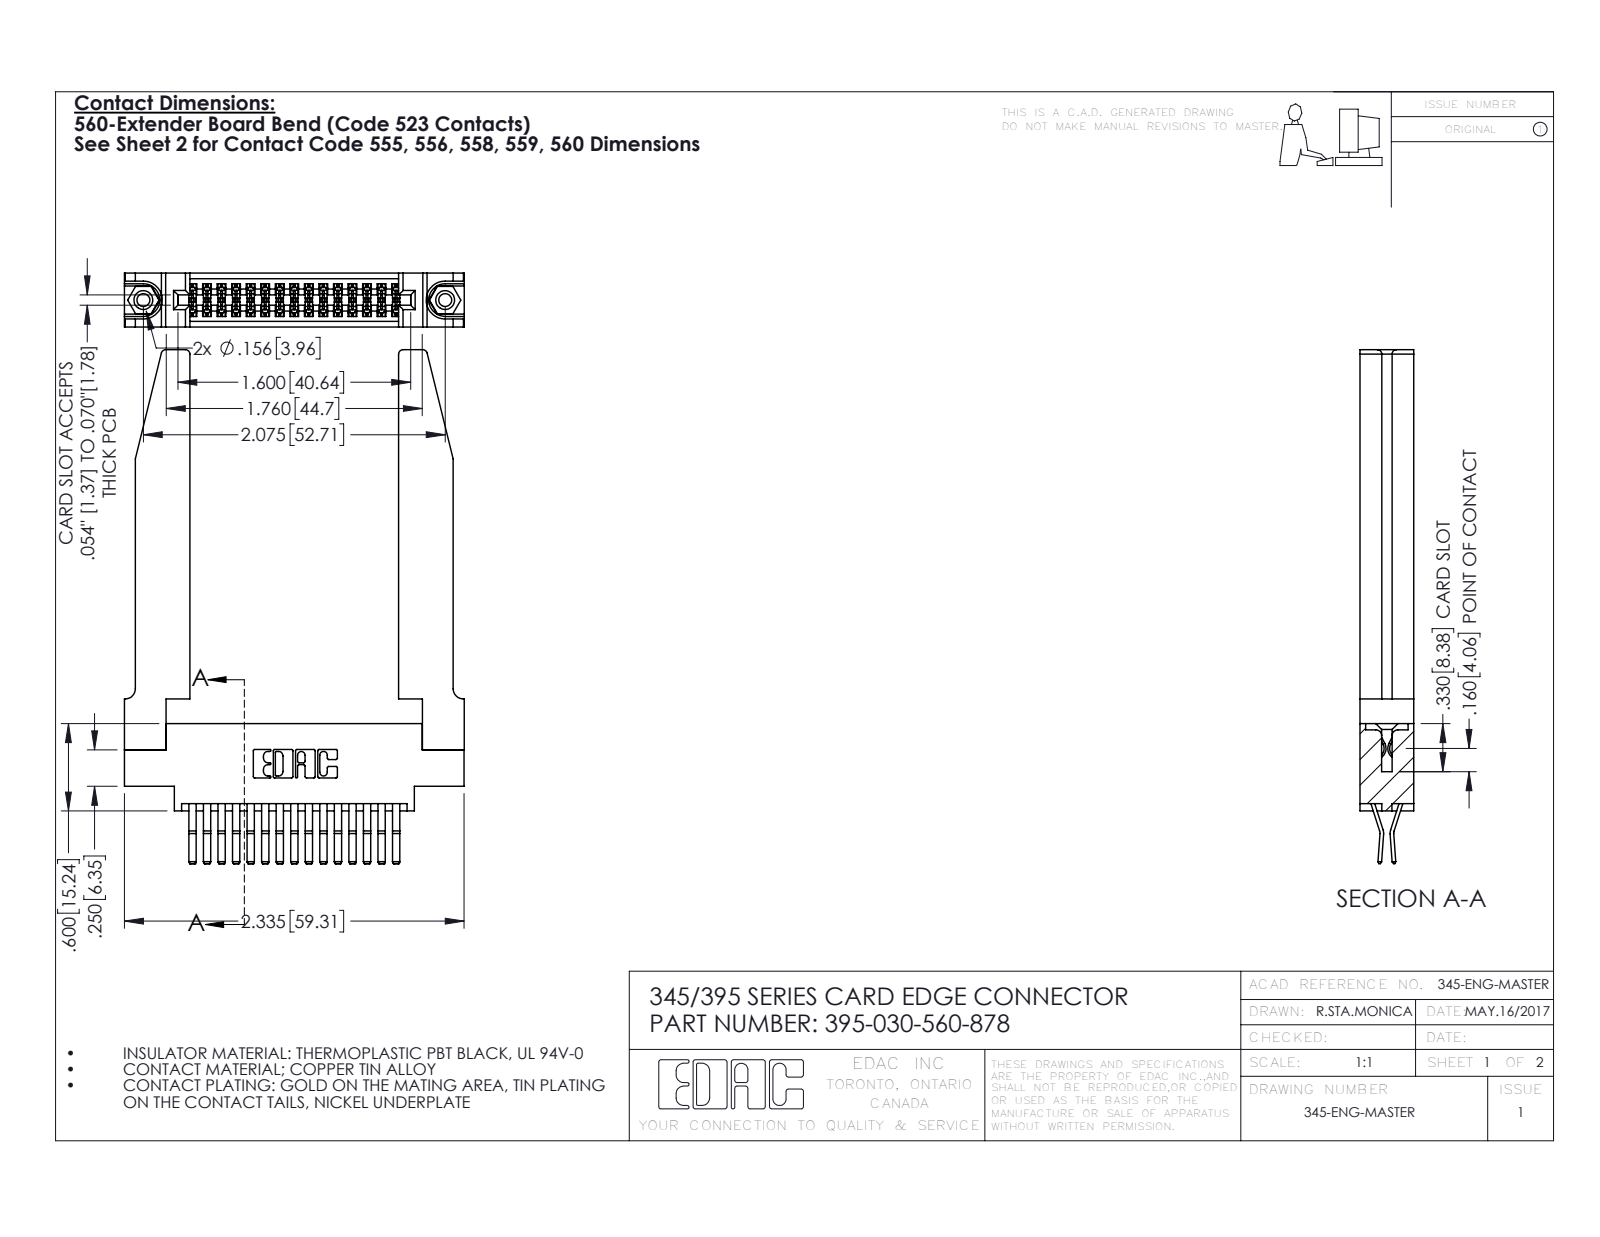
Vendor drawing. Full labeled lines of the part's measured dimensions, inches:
Part name (STEP PRODUCT): 345-292-001_560 Tail; 345-220-078_345-220-078; 395-030-560-878; 345 Part_0.170 Offset - 0.156 Dia-TH (+1 more)
STEP written by: SolidWorks 2016 (CONFIG_CONTROL_DESIGN)
Units: inches
Bodies: 35 solids, 1924 faces (1216 planar, 656 cylindrical, 52 other)
Overall size (bounding box): 3.532 × 2.336 × 0.37
Volume: 0.816 in³ · Surface area: 23.62 in²
Round holes (diameter × count): ⌀0.089 ×2, ⌀0.125 ×2, ⌀0.156 ×2, ⌀0.064 ×1
Round bosses / shafts (diameter × count): ⌀0.155 ×2
Partial cylindrical surfaces — rounded edges, fillets, slot ends (radius × count): R0.006 ×45, R0.01 ×22, R0.03 ×8, R0.007 ×6, R0.031 ×6, R0.026 ×3, R0.01 ×2, R0.014 ×2
Main face-to-face distances: 0.37, 0.072, 0.298, 0.025, 0.15, 0.148, 0.22, 0.077, 0.123, 0.098
Hole centre spacings: 0.27, 1.842, 2.075
